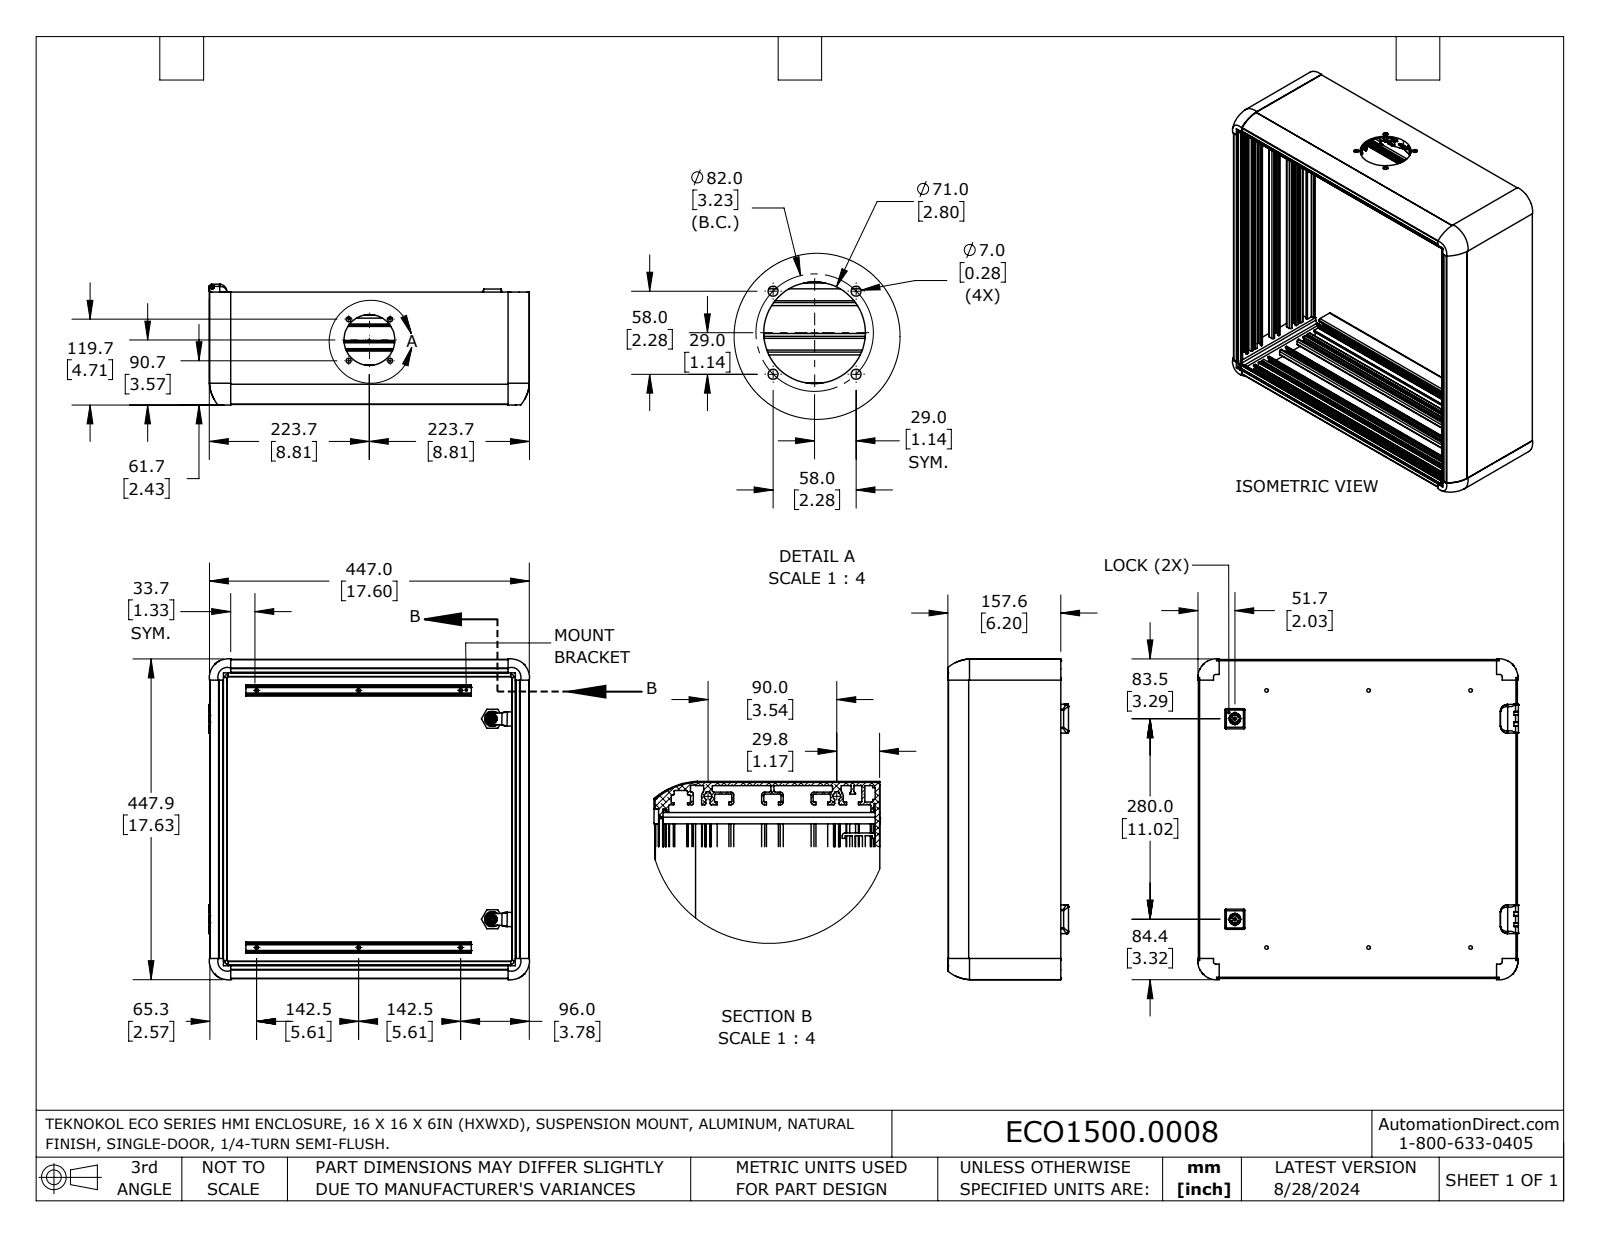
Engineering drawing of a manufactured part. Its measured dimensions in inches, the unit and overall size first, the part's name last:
Units: inches
Overall size (bounding box): 17.652 × 17.634 × 6.637
Round holes (diameter × count): ⌀0.197 ×6, ⌀0.169 ×5, ⌀0.276 ×4, ⌀0.63 ×2, ⌀2.795 ×1
Round bosses / shafts (diameter × count): ⌀0.371 ×6, ⌀0.197 ×6, ⌀0.614 ×2, ⌀0.531 ×2, ⌀0.175 ×2, ⌀0.157 ×1
Partial cylindrical surfaces — rounded edges, fillets, slot ends (radius × count): R0.02 ×259, R0.008 ×114, R0.079 ×65, R0.039 ×58, R0.098 ×36, R0.01 ×24, R0.016 ×20, R0.006 ×12
Main face-to-face distances: 0.118, 0.089, 17.453, 17.542, 17.365, 0.354, 0.079, 0.531, 0.236, 0.325
Hole centre spacings: 1.615, 2.283, 5.61, 15.167, 15.207, 11.024, 14.134, 1.181
Volume: 150.6 in³ · Surface area: 2 571 in²
Bodies: 13 solids, 3064 faces (1150 planar, 1116 cylindrical, 798 other)
Part name (STEP PRODUCT): ECO.1500.0008(400x400) (2)
STEP written by: SolidWorks 2023 (AUTOMOTIVE_DESIGN)
